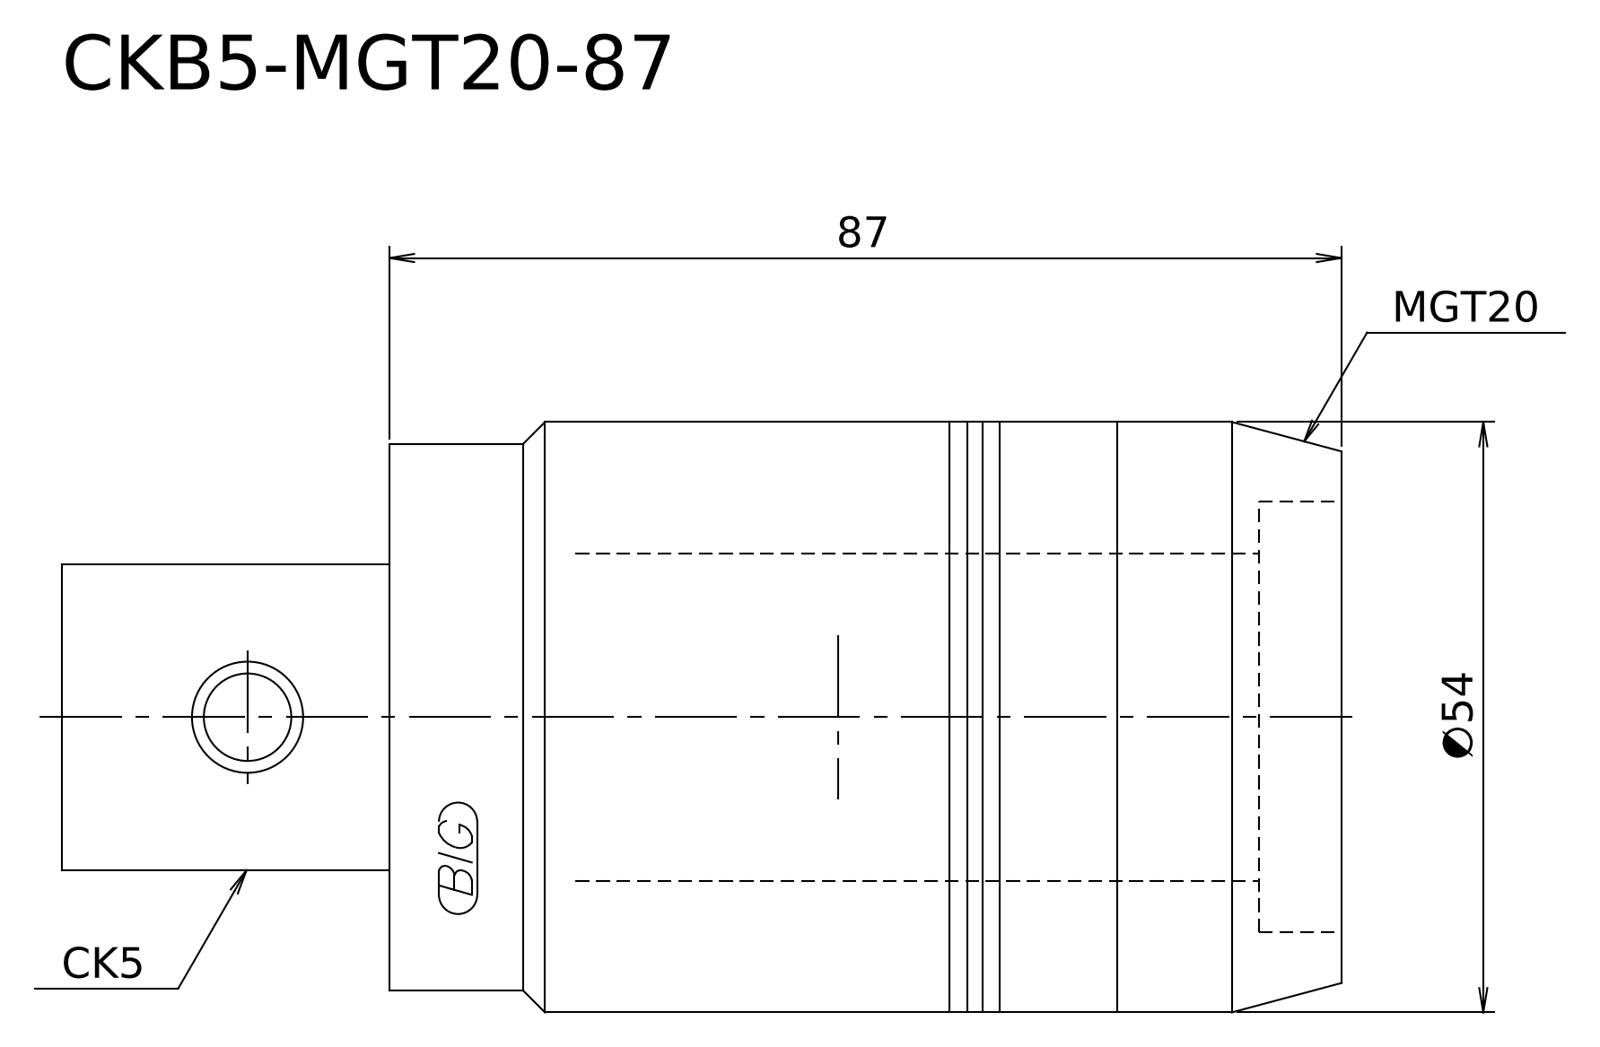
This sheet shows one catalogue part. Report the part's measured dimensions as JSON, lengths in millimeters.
{"step_written_by": "Kubotek KeyCreator V8.5.1 (14335) (CONFIG_CONTROL_DESIGN)", "units": "millimeters", "bodies": {"solids": 1, "faces": 14, "planar": 2, "cylindrical": 6, "other": 6}, "overall_size": [87, 54, 54], "volume_mm3": 192573, "surface_area_mm2": 18629, "round_bosses_or_shafts": [[54, 1], [53.2, 1], [50, 1]], "face_to_face_distances": [87]}
